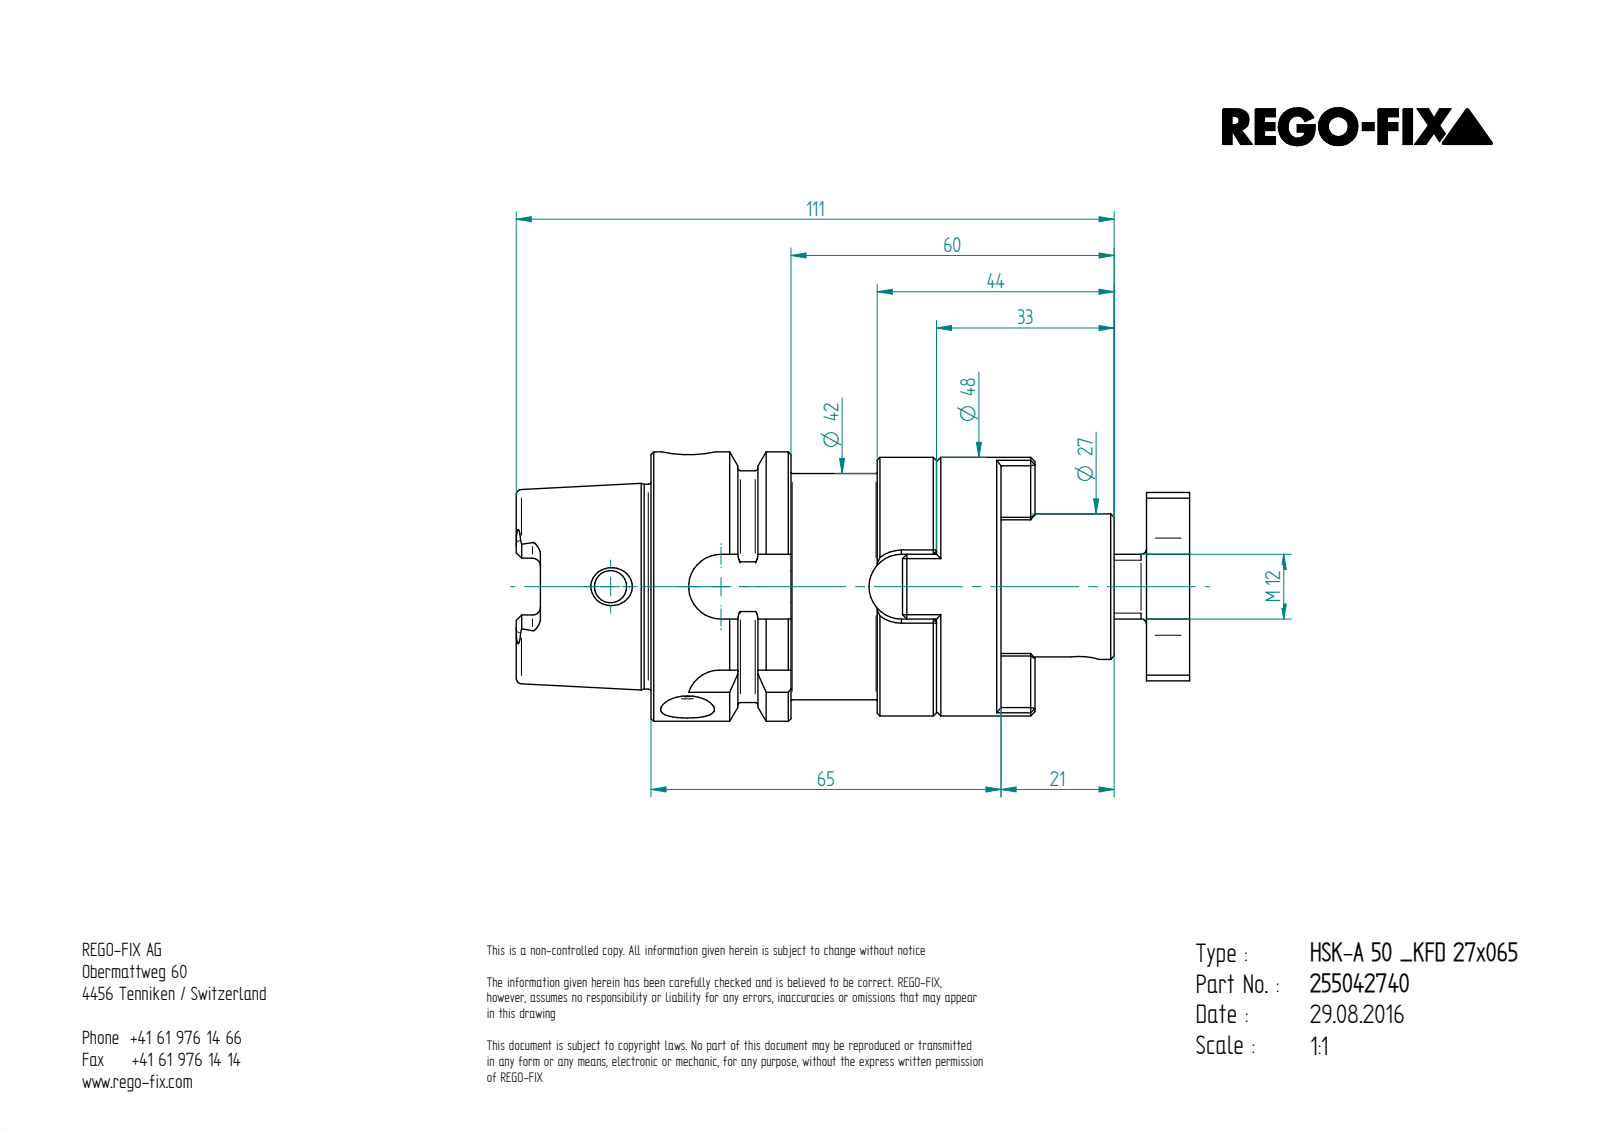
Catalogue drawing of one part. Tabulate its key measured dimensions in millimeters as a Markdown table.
| quantity | value |
| --- | --- |
| STEP written by | Unknown (AUTOMOTIVE_DESIGN) |
| units | millimeters |
| bodies | 1 solid, 279 faces (142 planar, 55 cylindrical, 82 other) |
| overall size | 125 × 50 × 50 |
| volume | 127 971 mm³ |
| surface area | 29 372 mm² |
| round holes (diameter × count) | 10 × 2, 5 × 1, 6 × 1, 6.8 × 1, 10.11 × 1, 13 × 1, 14.92 × 1, 17 × 1, 26 × 1, 27 × 1, 32 × 1 |
| round bosses / shafts (diameter × count) | 50 × 1, 48 × 1, 43 × 1, 42 × 1, 38.01 × 1, 26.4 × 1, 12 × 1 |
| partial cylindrical surfaces (radius × count) | 1.5 × 6, 6 × 5, 2.38 × 4, 3 × 4, 3.5 × 2, 17.5 × 1 |
| main face-to-face distances | 27, 35, 8, 12, 16, 65, 100, 66, 39, 92 |
